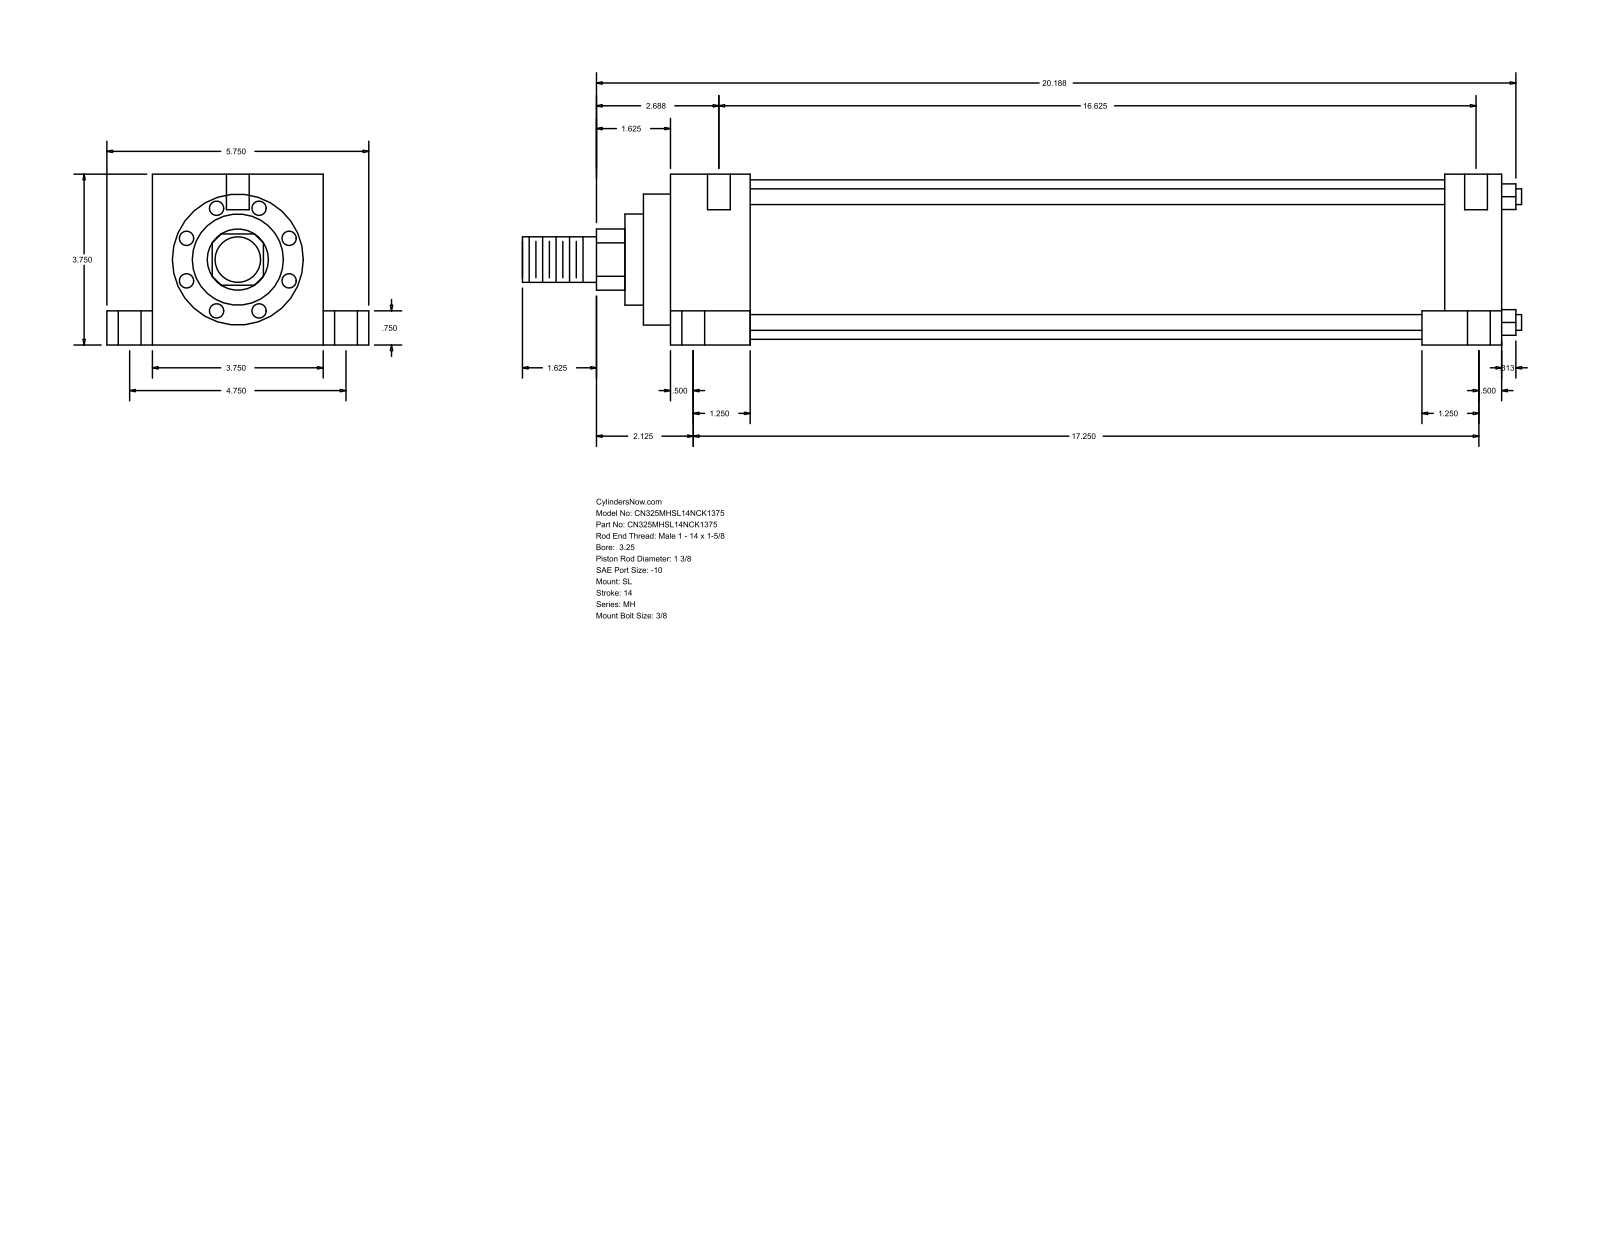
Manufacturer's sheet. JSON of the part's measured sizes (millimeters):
{"part_name": "MH_SL__0325_1.375", "step_written_by": "GSSL Pune (CONFIG_CONTROL_DESIGN)", "units": "millimeters", "bodies": {"solids": 0, "faces": 110, "planar": 77, "cylindrical": 33, "other": 0}, "overall_size": [557.21, 146.05, 95.25], "round_holes": [[12.7, 6], [5.56, 4], [19.05, 4]], "round_bosses_or_shafts": [[8.76, 4], [88.9, 1], [73.03, 1], [50.8, 1], [34.92, 1], [25.4, 1]], "partial_cylinders_radius": [[17.06, 1]], "face_to_face_distances": [95.24, 463.55, 44.45, 419.1, 25.41, 120.65, 19.05, 76.19, 431.8, 387.35], "hole_center_spacings": [60.35, 60.41, 61.65, 62, 120.66, 428.13, 428.63, 429.71]}
